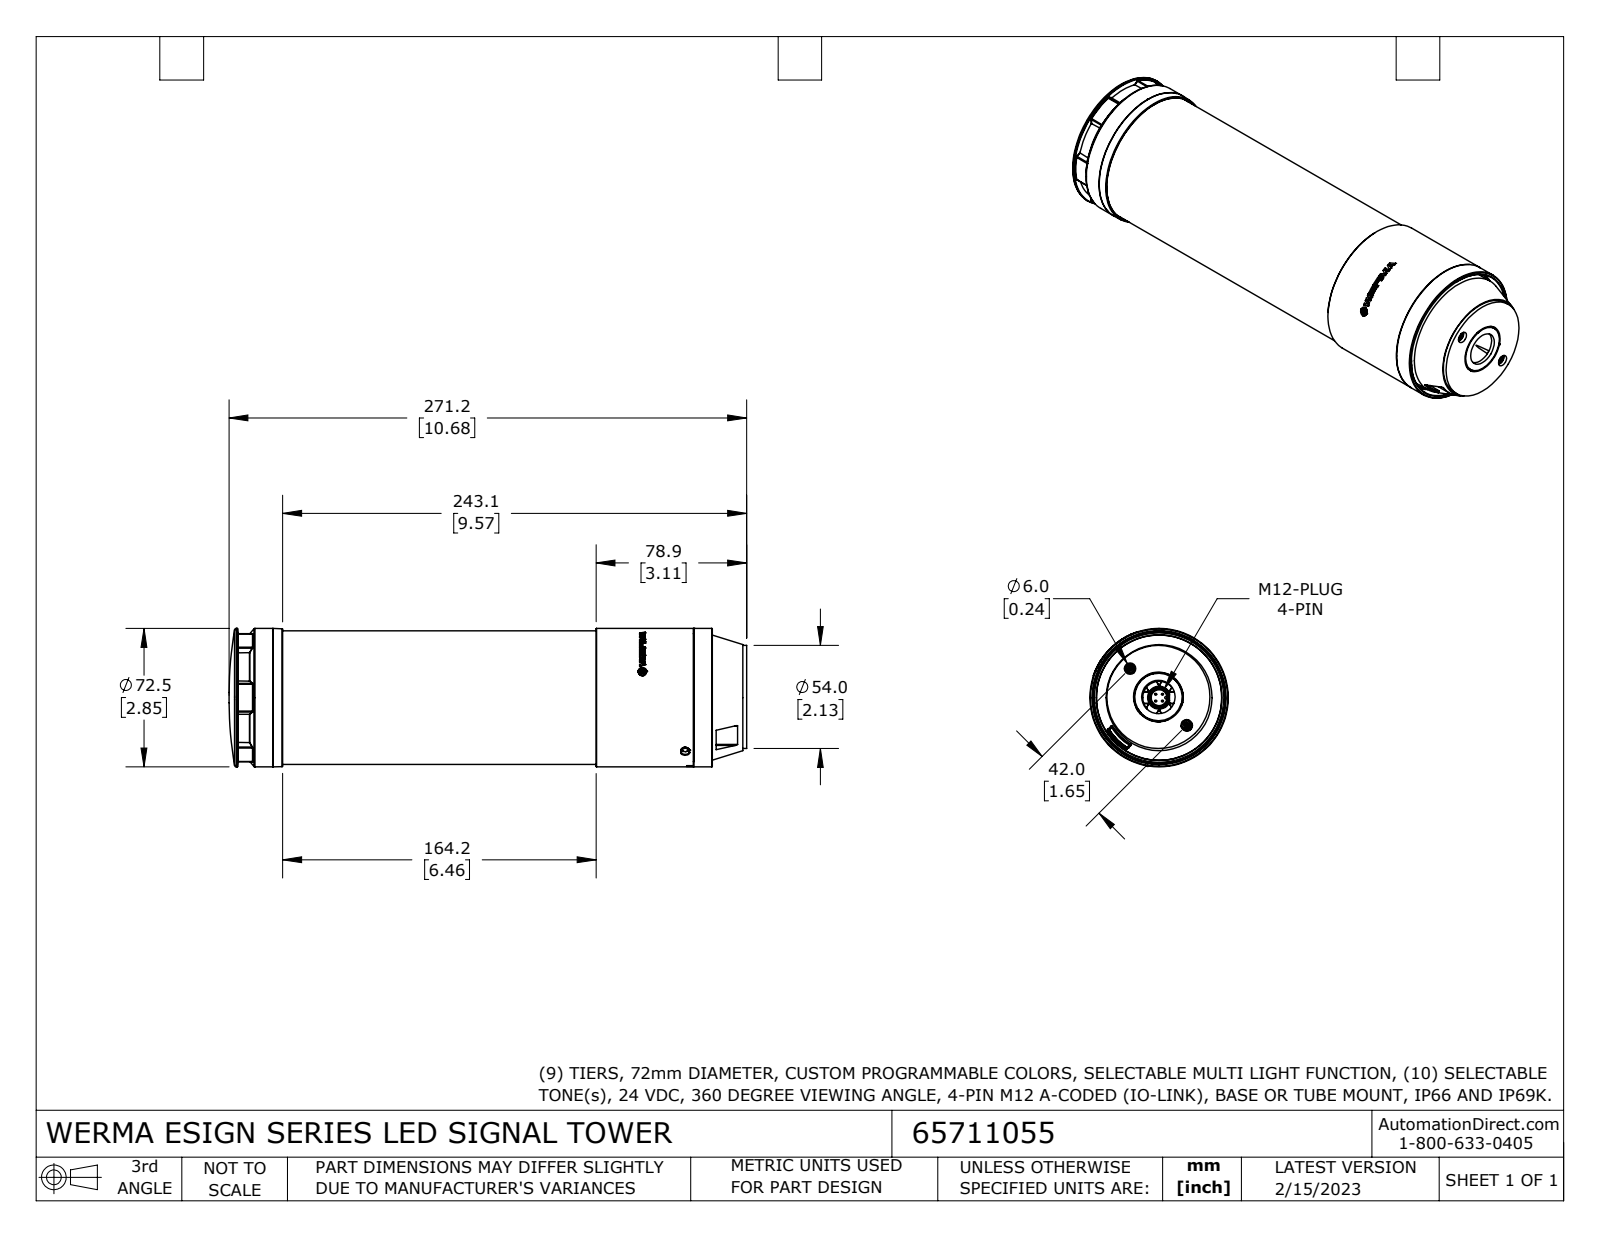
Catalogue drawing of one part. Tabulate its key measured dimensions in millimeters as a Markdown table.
| quantity | value |
| --- | --- |
| part name | 65711055 |
| STEP written by | SolidWorks 2021 (CONFIG_CONTROL_DESIGN) |
| units | millimeters |
| bodies | 1 solid, 846 faces (296 planar, 176 cylindrical, 374 other) |
| overall size | 271.2 × 72.5 × 72.5 |
| volume | 960 000 mm³ |
| surface area | 105 100 mm² |
| round holes (diameter × count) | 6 × 2, 4.3 × 1, 8.3 × 1, 17.5 × 1, 25.1 × 1, 26 × 1 |
| round bosses / shafts (diameter × count) | 1 × 4, 72.5 × 1, 70 × 1, 54 × 1, 24.9 × 1, 12 × 1, 10.5 × 1, 4.4 × 1 |
| partial cylindrical surfaces (radius × count) | 0.3 × 21, 0.3 × 12, 0.7 × 12, 2 × 8, 1.5 × 6, 2 × 2, 2.2 × 2, 2.5 × 2 |
| main face-to-face distances | 234.8, 25.7, 260.5, 5, 20.7, 255.5, 3, 222.6, 2, 23.7 |
| hole center spacings | 21, 0.5, 20.5, 21.5, 42 |
